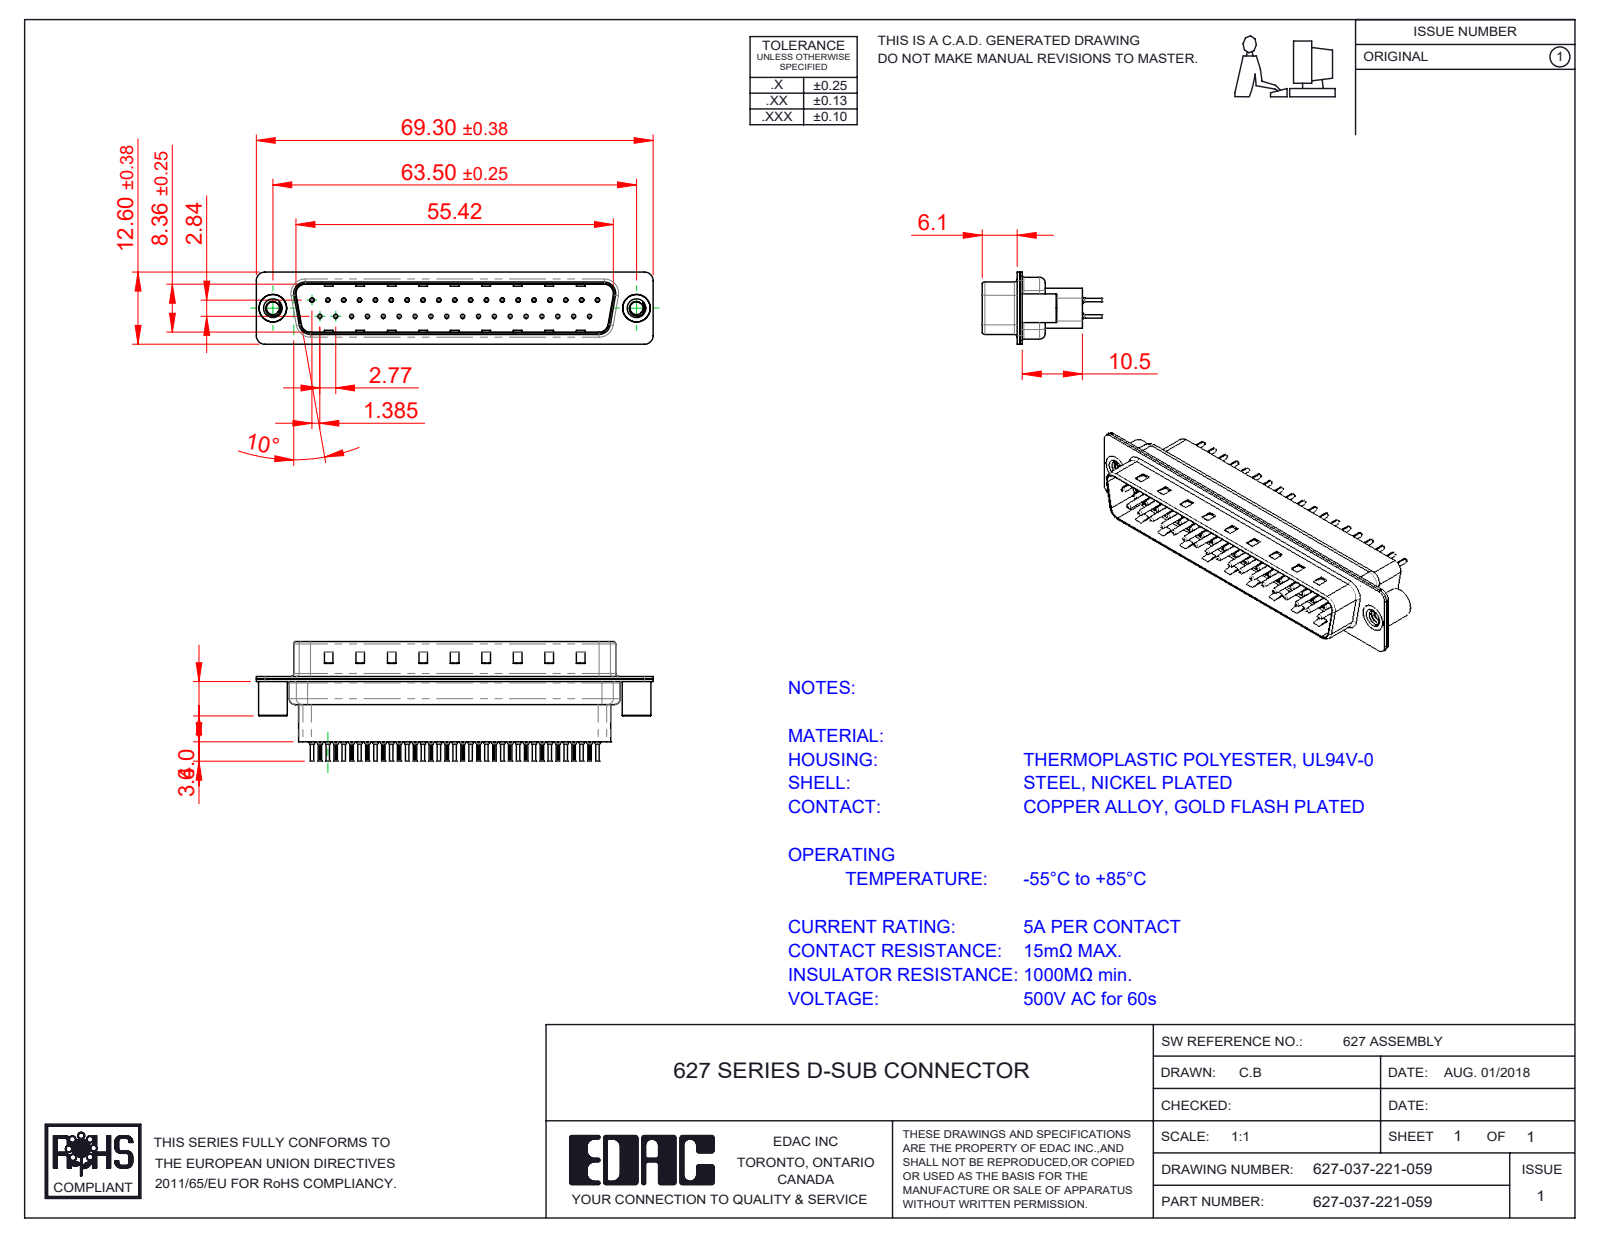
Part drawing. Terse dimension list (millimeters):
name: 627 Shell Front_37 Contacts; 627 Contact Row 2_21H; 627 Shell Rear_37 Contacts; 627 Housing_37 HP (+3 more)
written by: SolidWorks 2020 (CONFIG_CONTROL_DESIGN)
unit: mm
bodies: 42 solids, 4060 faces (1091 planar, 1530 cylindrical, 1439 other)
size: 69.3 × 20.8 × 12.6
volume: 5 403 mm³; area: 13 750 mm²
holes: 37× ⌀0.2, 37× ⌀0.35, 37× ⌀1.1, 37× ⌀1.6, 2× ⌀2.26, 2× ⌀4, 2× ⌀4.8
bosses: 37× ⌀2, 37× ⌀1.5, 37× ⌀0.75, 37× ⌀0.6, 2× ⌀5, 2× ⌀4.9
rounds: 74× R0.1, 16× R1.5, 12× R2, 8× R0.5, 8× R1.6, 4× R0.25, 4× R0.6, 4× R0.65
face distances: 0.4, 0.82, 9.58, 0.68, 7.68, 0.45, 1.5, 1.08, 8.08, 8.76
hole spacings: 3.16, 2.77, 5.54, 8.31, 5.04, 10.1, 11.08, 12.78
